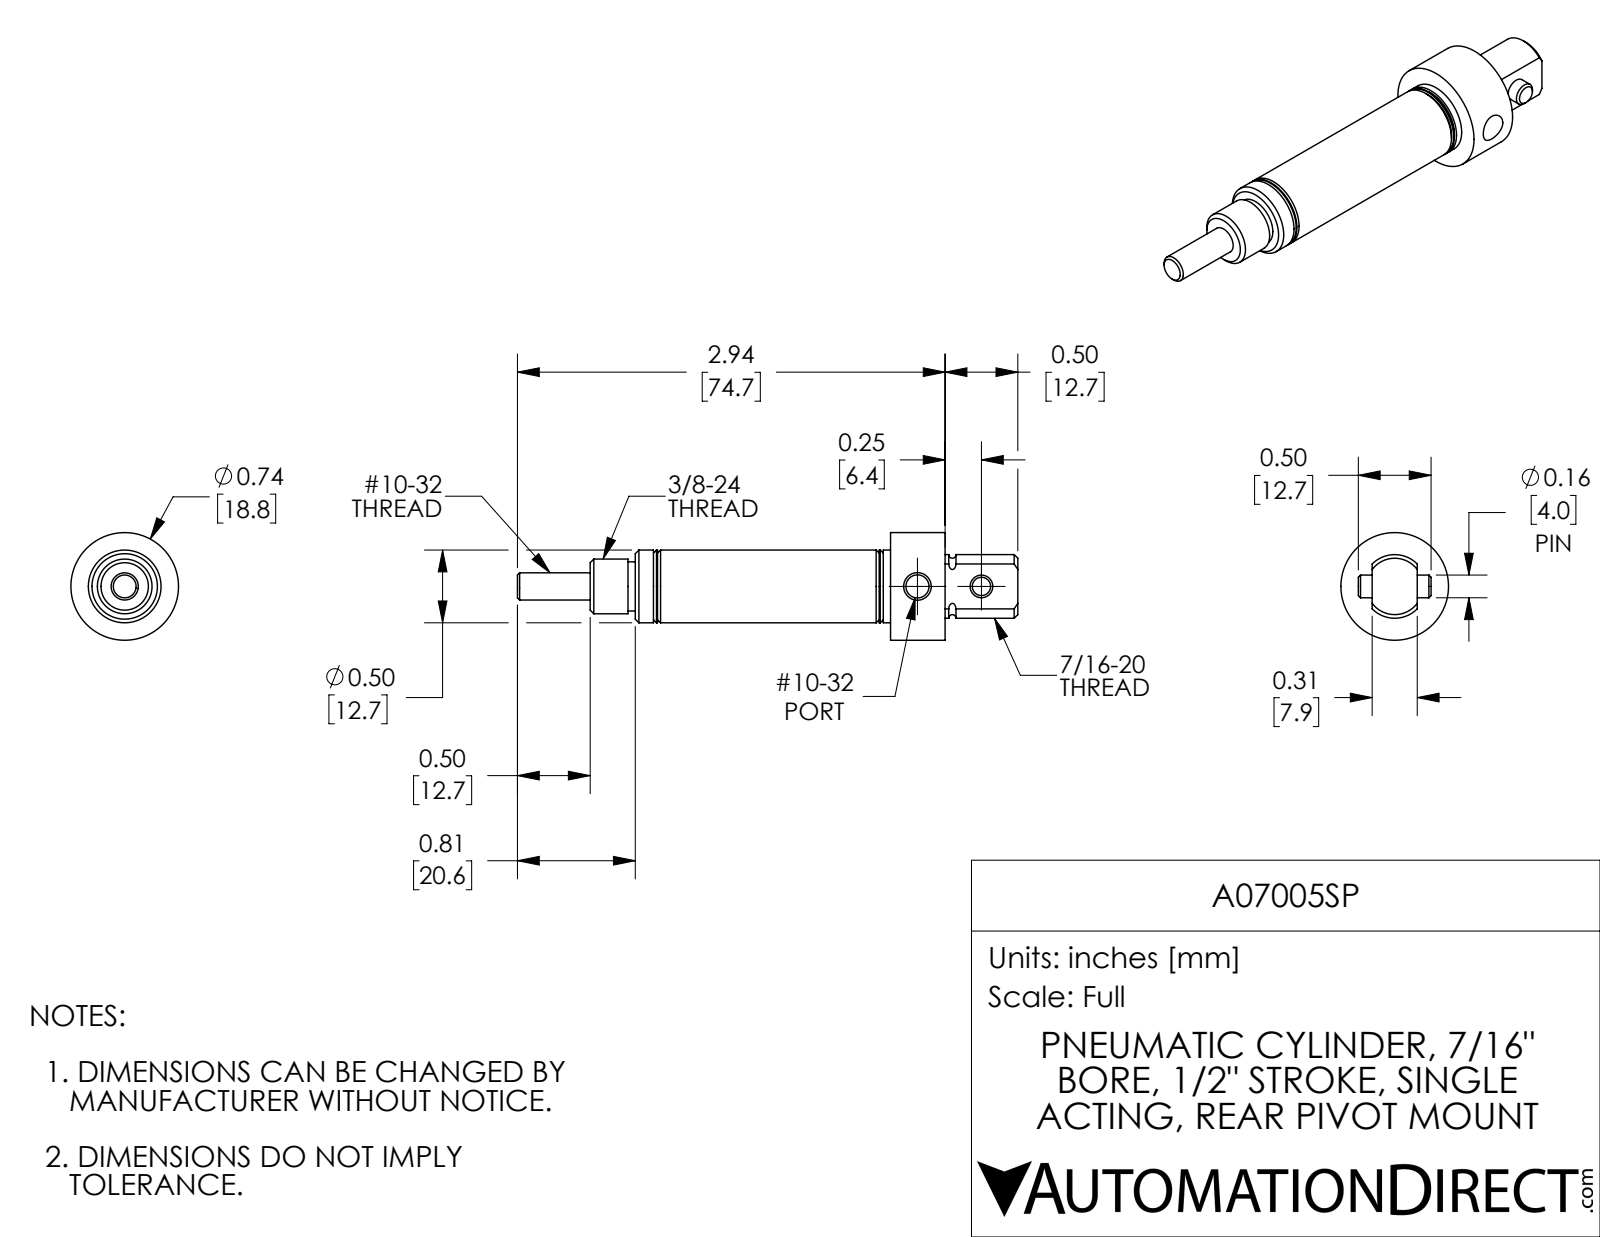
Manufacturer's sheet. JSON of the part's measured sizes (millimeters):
{"part_name": "A07005SP-Rod; A07005SP-Pin; A07005SP-MainBody; A07005SP", "step_written_by": "SolidWorks 2017 (AUTOMOTIVE_DESIGN)", "units": "millimeters", "bodies": {"solids": 3, "faces": 82, "planar": 20, "cylindrical": 36, "other": 26}, "overall_size": [87.4, 18.8, 18.8], "volume_mm3": 8870, "surface_area_mm2": 6806, "round_holes": [[4, 1], [4, 1], [4.7, 1], [4.8, 1]], "round_bosses_or_shafts": [[18.8, 1], [12.7, 1], [11.1, 1], [9.6, 1], [8.6, 1]], "face_to_face_distances": [12.7, 14.4, 9.5, 4.8, 27.1, 39.8, 22.2, 52.5, 7.9, 17.5], "hole_center_spacings": [11.2]}
